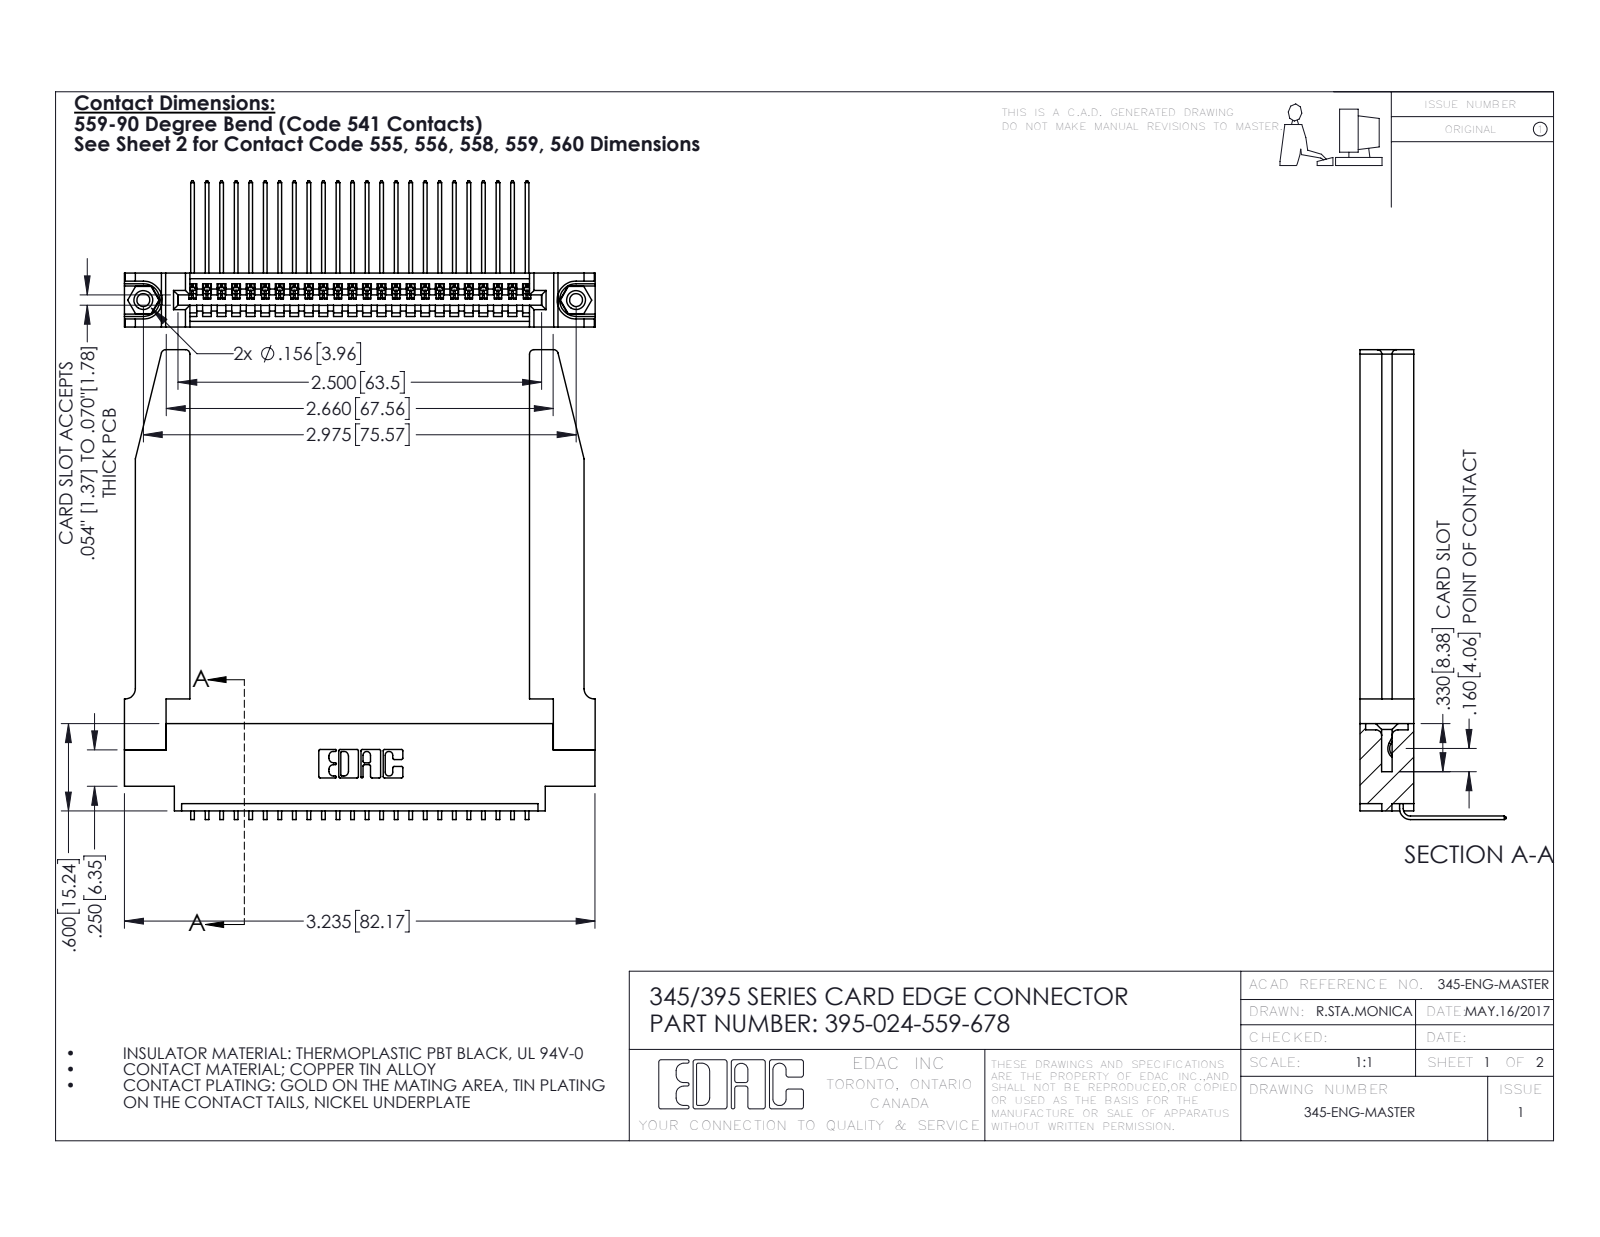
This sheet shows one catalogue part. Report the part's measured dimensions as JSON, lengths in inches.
{"part_name": "345-250-001_345-250-001-102; 345 Part_0.170 Offset - 0.156 Dia-TH; 345-292-001_558 559 Tail - 1; 395-024-559-678 (+1 more)", "step_written_by": "SolidWorks 2016 (CONFIG_CONTROL_DESIGN)", "units": "inches", "bodies": {"solids": 29, "faces": 1804, "planar": 1234, "cylindrical": 518, "other": 52}, "overall_size": [3.236, 3.229, 1.005], "volume_in3": 0.94, "surface_area_in2": 26.86, "round_holes": [[0.089, 2], [0.125, 2], [0.156, 2], [0.064, 1]], "round_bosses_or_shafts": [[0.155, 2]], "partial_cylinders_radius": [[0.006, 48], [0.01, 22], [0.03, 8], [0.007, 6], [0.031, 6], [0.026, 3], [0.031, 2], [0.04, 2]], "face_to_face_distances": [0.37, 0.072, 0.298, 0.098, 0.272, 0.025, 0.2, 0.148, 0.15, 0.123], "hole_center_spacings": [0.27, 2.741, 2.975]}
